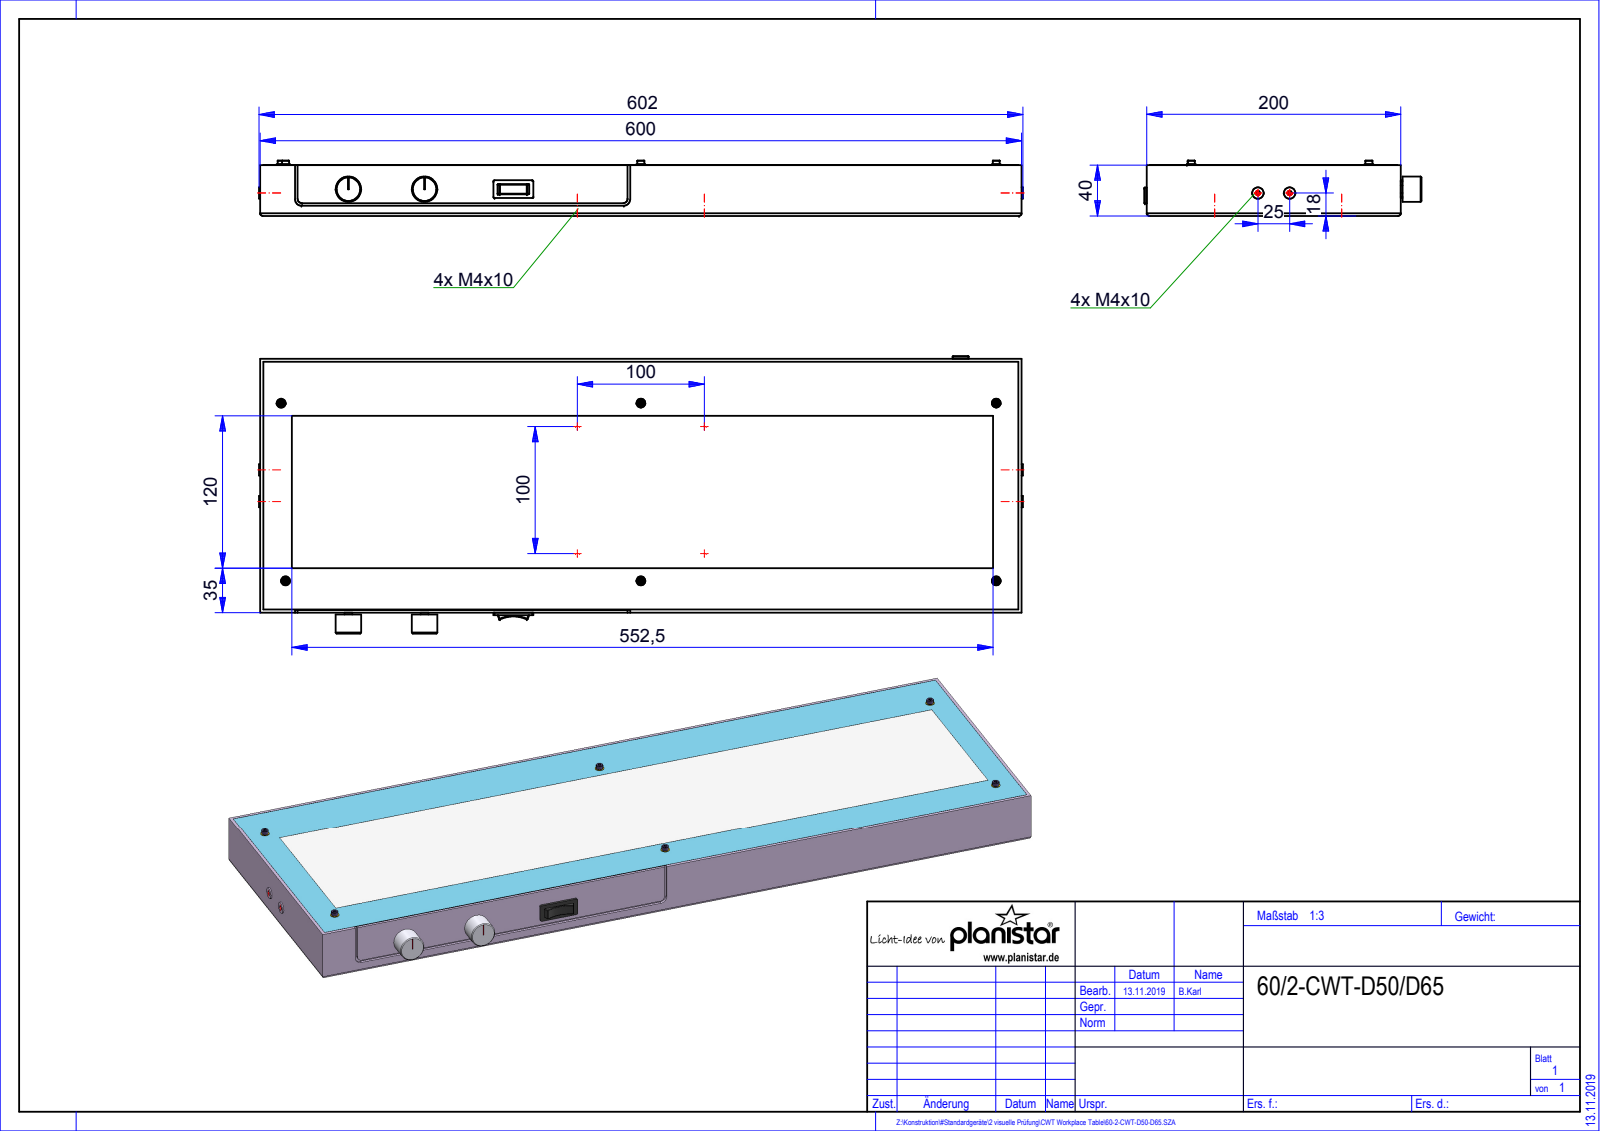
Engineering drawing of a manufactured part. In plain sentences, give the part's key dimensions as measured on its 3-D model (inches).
The part is named "Root; Baugruppe_Xled-2-VD; QUADER_0; ISO 14579-M3x10-10.9_Zylinderkopfschrauben (+4 more)". Its 3-D file was written by "HiCAD 2015 2002.1 Build 408 (AUTOMOTIVE_DESIGN)". It is 18 solids with 287 faces: 106 planar, 150 cylindrical and 31 other. Overall it measures 23.701 by 8.602 by 1.717 inches. Its volume is 293.9 cubic inches and its surface area 509.7 square inches. Round holes: 6 of diameter 0.126, 6 of diameter 0.13, 6 of diameter 0.157, 1 of diameter 0.22, 1 of diameter 0.394. Round bosses or shafts: 6 of diameter 0.276, 6 of diameter 0.217, 6 of diameter 0.118, 6 of diameter 0.097, 2 of diameter 0.787, 2 of diameter 0.354, 2 of diameter 0.236, 1 of diameter 0.496. Partial cylindrical surfaces (rounded edges, fillets, slot ends): 36 of radius 0.009, 36 of radius 0.023, 6 of radius 0.02, 4 of radius 0.039, 4 of radius 0.079, 2 of radius 0.138, 2 of radius 0.197, 1 of radius 0.957. The main face-to-face distances are 1.577, 1.579, 7.874, 0.079, 7.795, 23.622, 1.575, 0.138, 0.591, 7.933. The hole center spacings are 3.937, 5.512, 11.024, 12.325, 2.099, 2.143, 5.064, 5.173.
